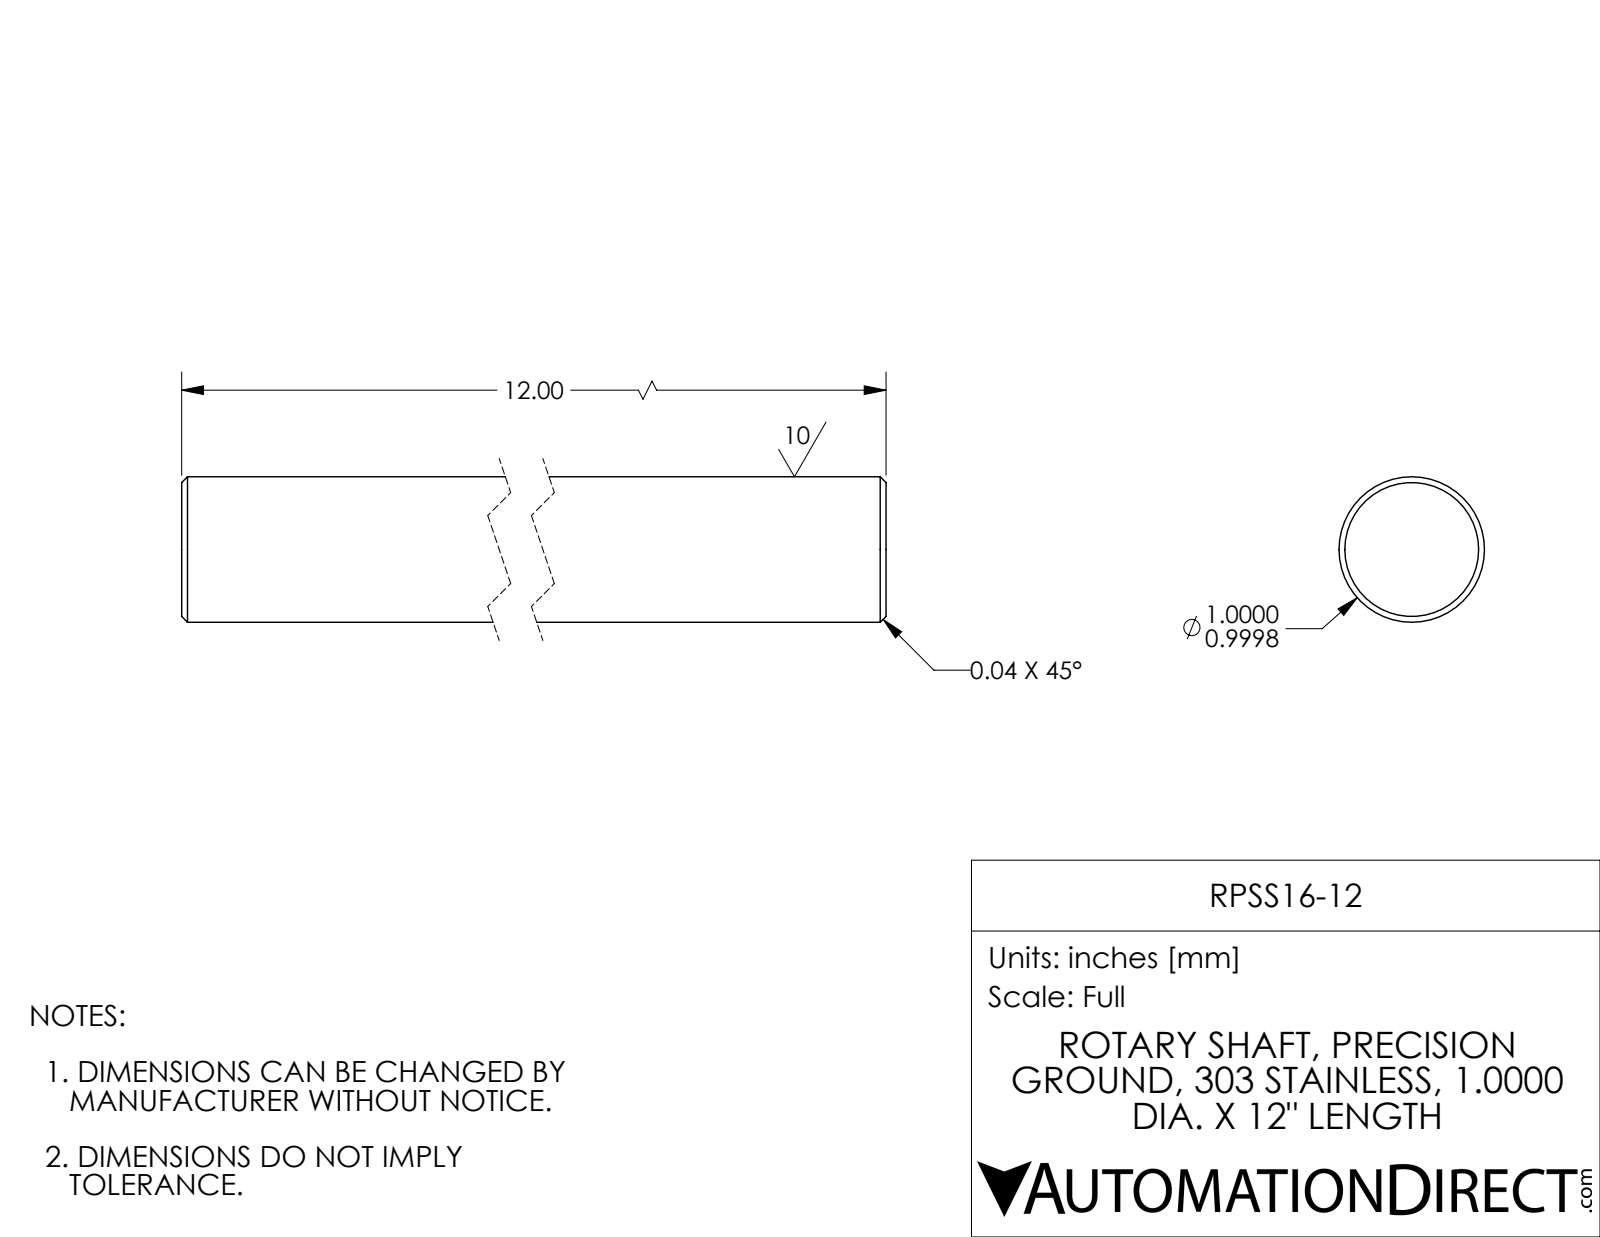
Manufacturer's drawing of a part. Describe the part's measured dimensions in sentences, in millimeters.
The part is named "RPSS16-12". Its 3-D file was written by "SolidWorks 2017 (AUTOMOTIVE_DESIGN)". It is 1 solid with 8 faces: 2 planar, 2 cylindrical and 4 other. Overall it measures 304.8 by 25.4 by 25.4 millimeters. Its volume is 154 400 cubic millimeters and its surface area 25 240 square millimeters. Round bosses or shafts: 1 of diameter 25.4. The main face-to-face distances are 304.8.
